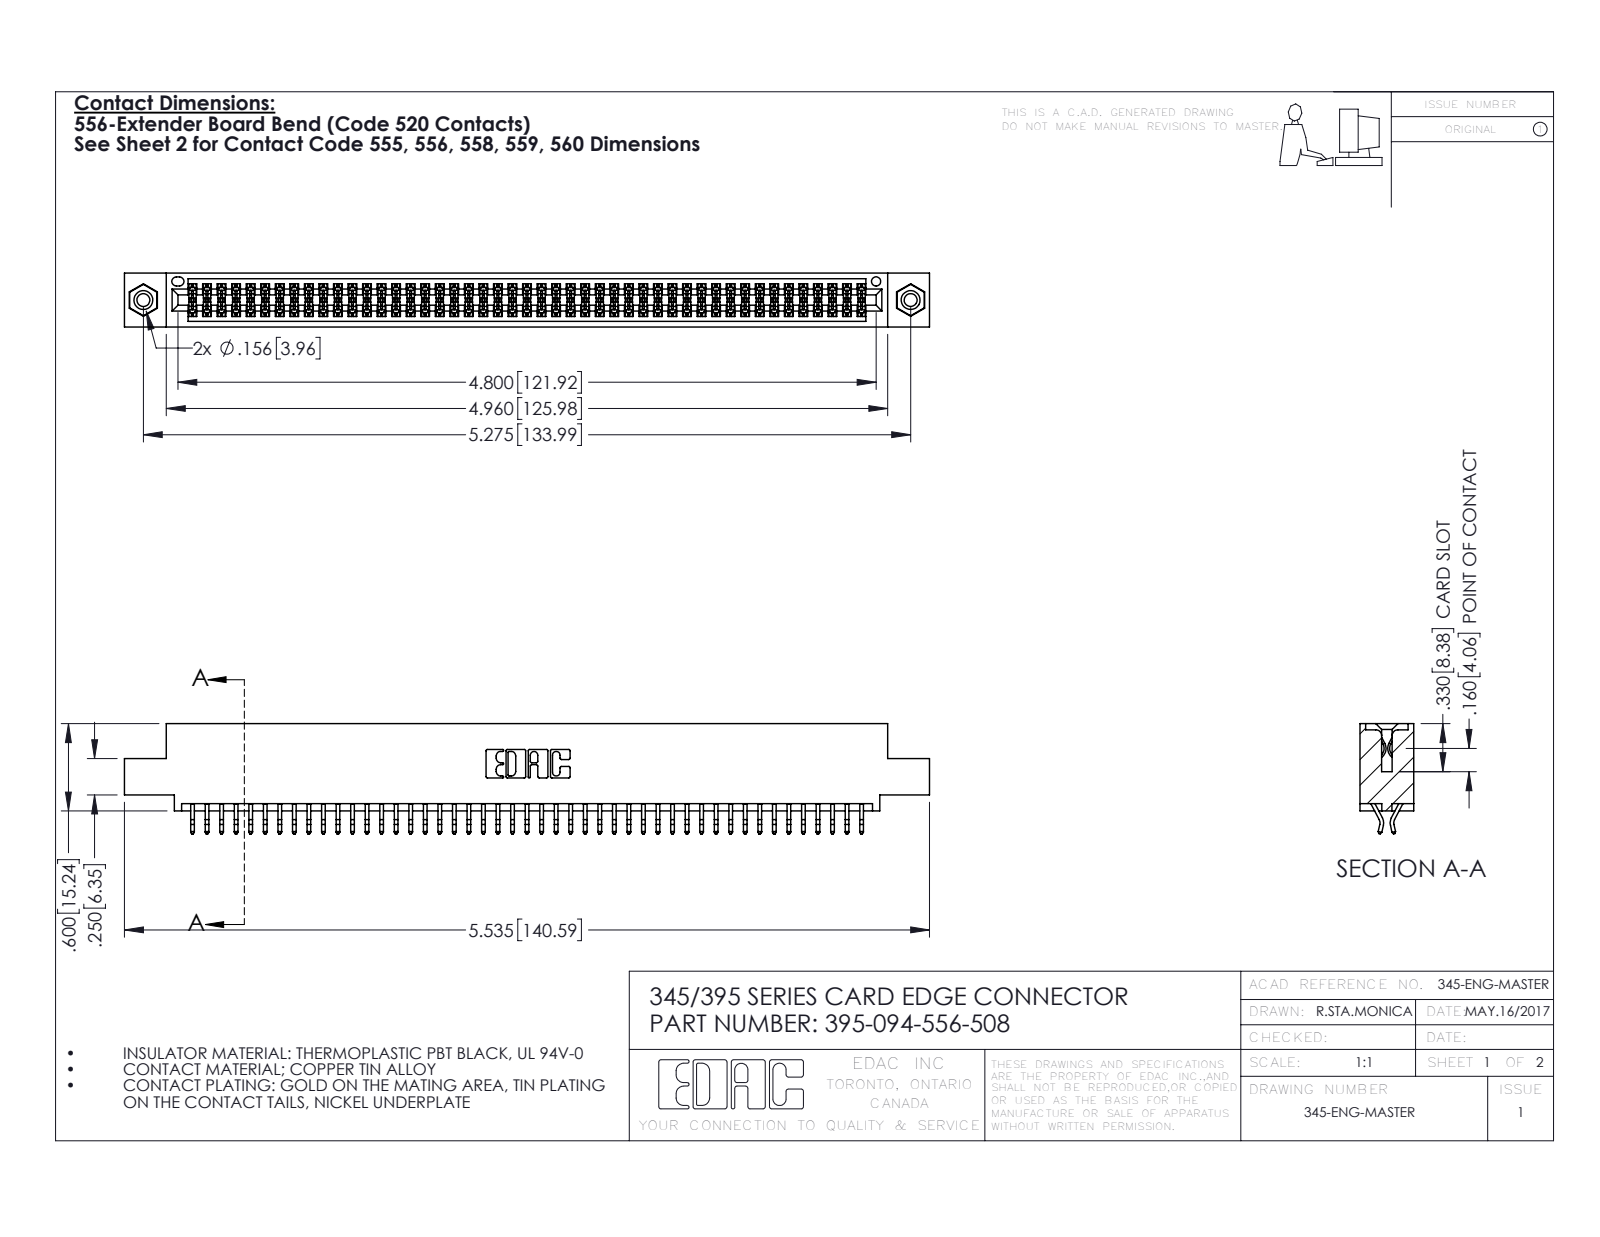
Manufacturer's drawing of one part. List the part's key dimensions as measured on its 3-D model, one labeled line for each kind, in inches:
Part name (STEP PRODUCT): 395-094-556-508; 345-292-001_556 Tail; 345-250-001_345-250-003-102; 345 Part_0.110 Offset - 0.156 Dia-TI
STEP written by: SolidWorks 2016 (CONFIG_CONTROL_DESIGN)
Units: inches
Bodies: 97 solids, 5454 faces (3594 planar, 1844 cylindrical, 16 other)
Overall size (bounding box): 5.535 × 0.757 × 0.37
Volume: 0.831 in³ · Surface area: 31.39 in²
Round holes (diameter × count): ⌀0.089 ×2, ⌀0.125 ×2, ⌀0.156 ×2, ⌀0.064 ×1
Round bosses / shafts (diameter × count): ⌀0.155 ×2
Partial cylindrical surfaces — rounded edges, fillets, slot ends (radius × count): R0.006 ×141, R0.01 ×22, R0.007 ×6, R0.031 ×6, R0.026 ×3, R0.01 ×2, R0.014 ×2, R0.019 ×2
Main face-to-face distances: 0.072, 0.298, 0.37, 0.2, 0.025, 0.098, 0.272, 0.225, 0.175, 0.149
Hole centre spacings: 0.27, 5.039, 5.275
